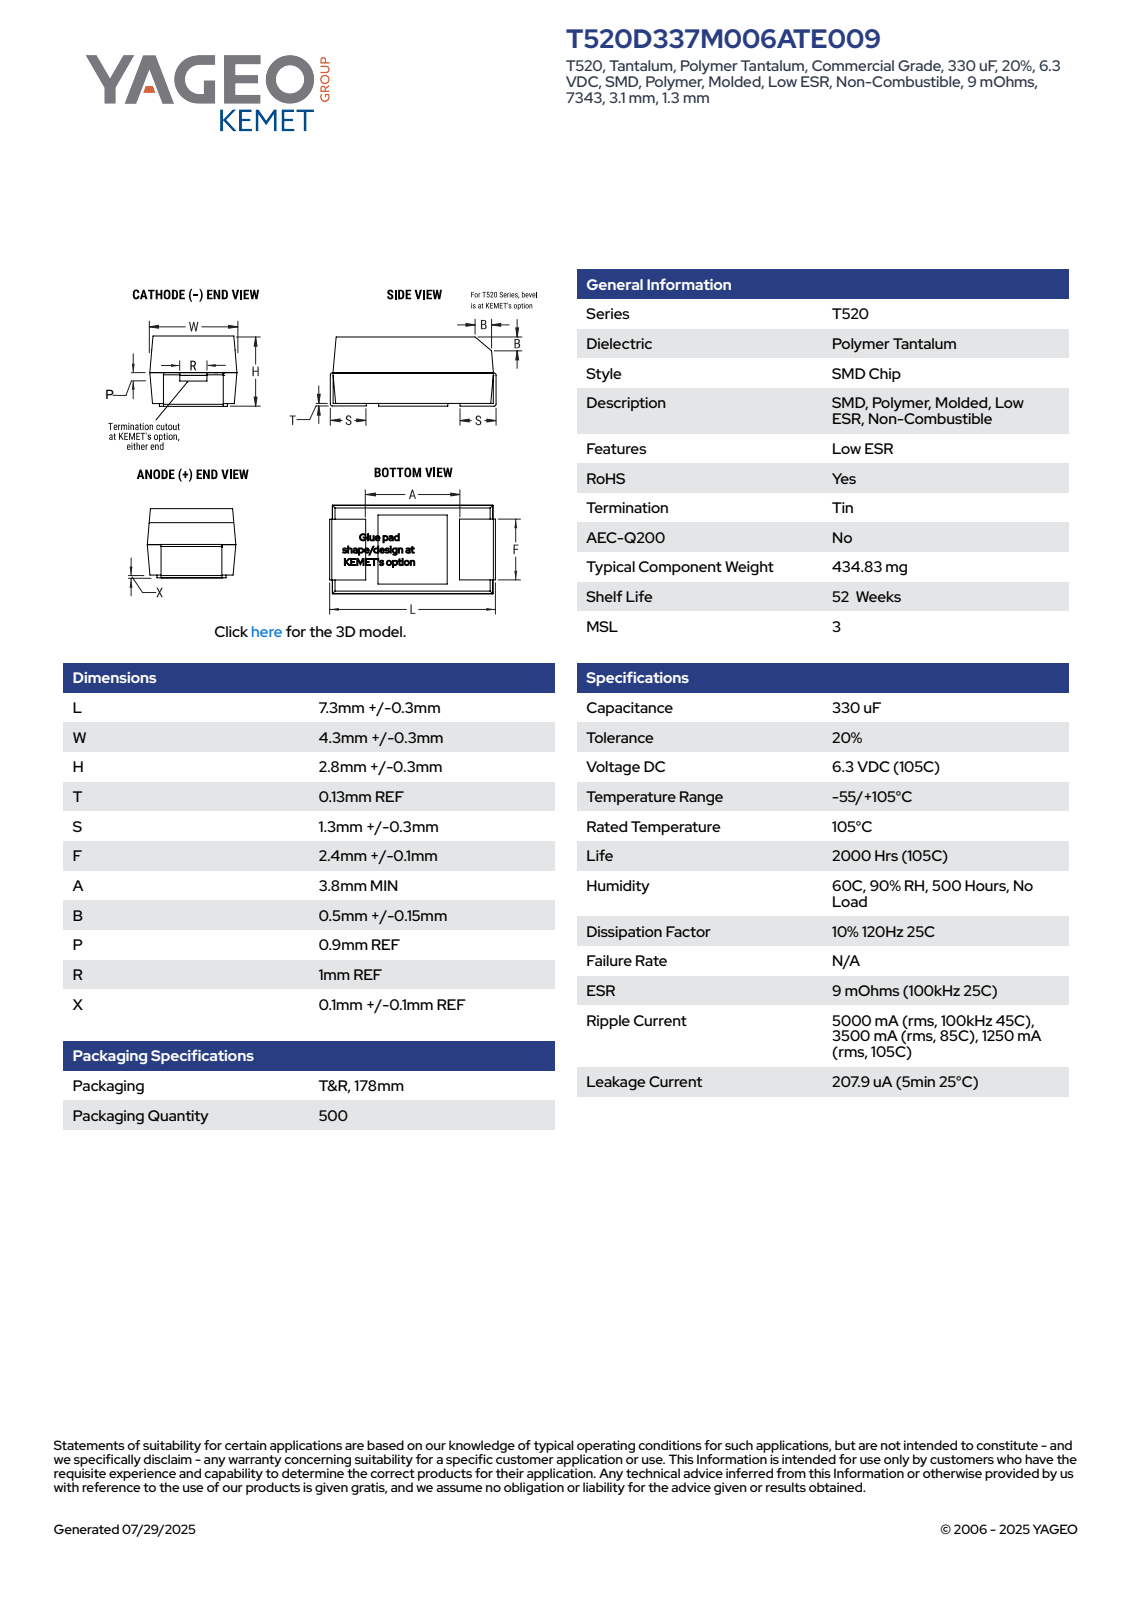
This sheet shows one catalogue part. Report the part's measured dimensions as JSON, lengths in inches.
{"part_name": "Case_Cathode_21; Case_Anode_21; CTS_7343_L7.60W4.60H3.10S1.3F2.4R1P0.9B0.5; Case_Top_21 (+1 more)", "step_written_by": "SolidWorks 2014 (AUTOMOTIVE_DESIGN)", "units": "inches", "bodies": {"solids": 4, "faces": 43, "planar": 38, "cylindrical": 5, "other": 0}, "overall_size": [0.299, 0.181, 0.122], "volume_in3": 0.006, "surface_area_in2": 0.35, "face_to_face_distances": [0.062, 0.055, 0.117, 0.18, 0.059, 0.121, 0.288, 0.06, 0.122, 0.294]}
